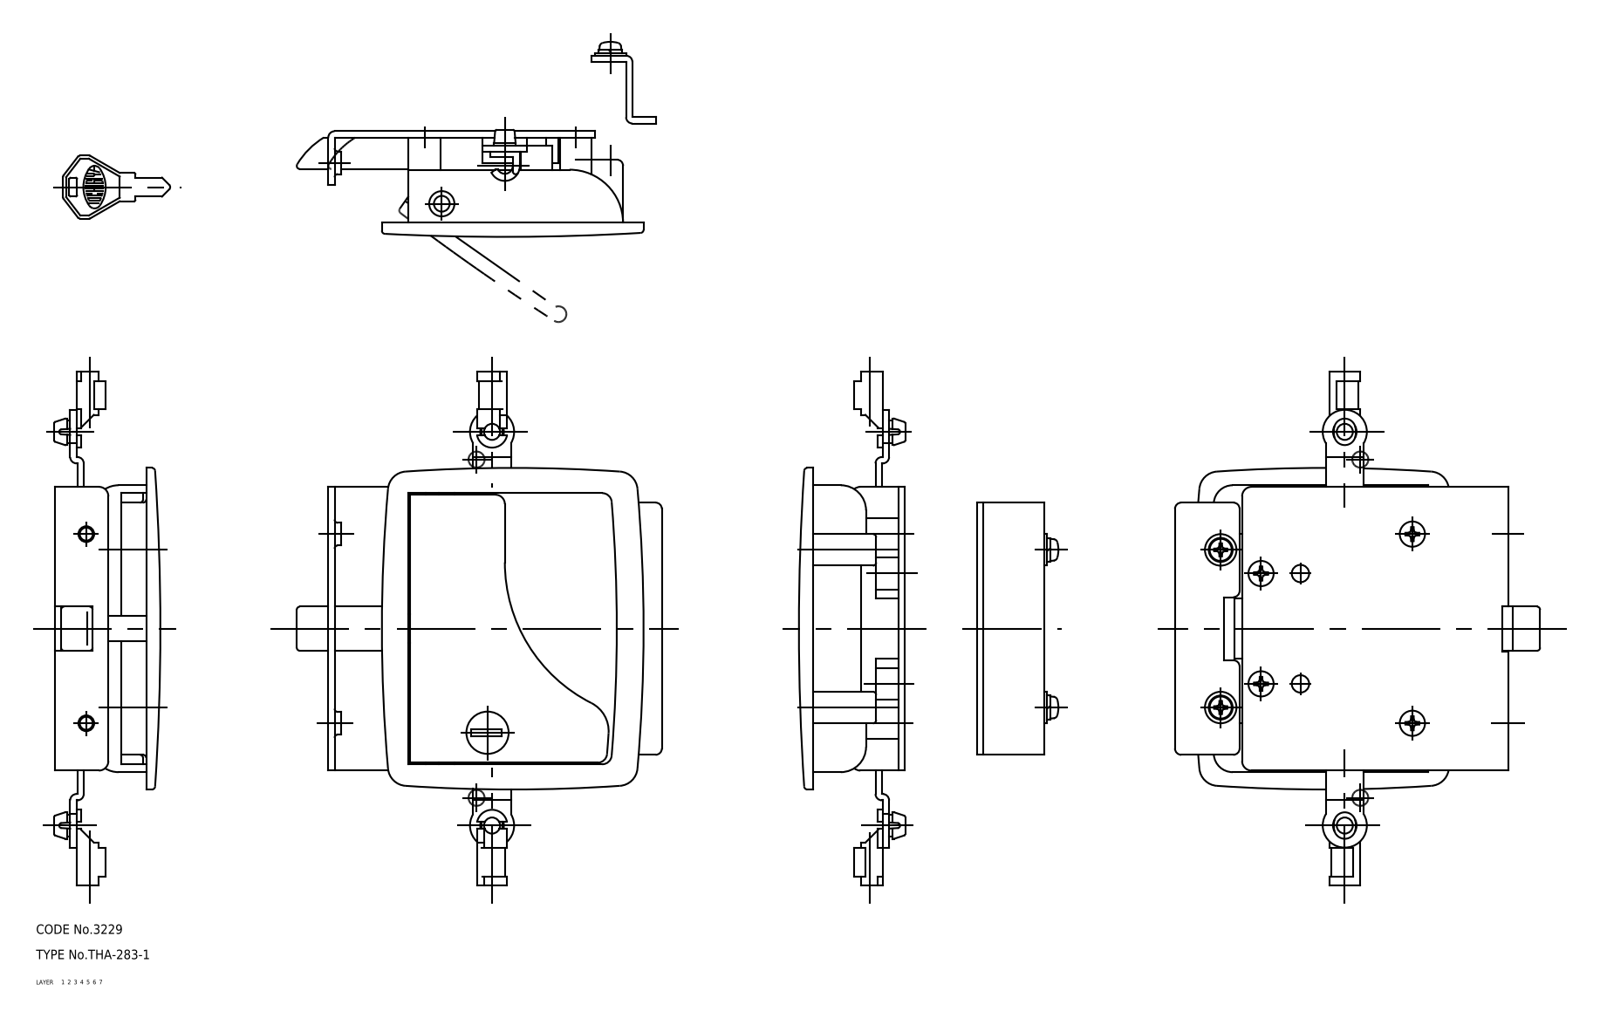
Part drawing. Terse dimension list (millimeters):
name: screw; bracket_B; holder_mr; holder (+8 more)
written by: CADfix (AUTOMOTIVE_DESIGN)
unit: mm
bodies: 15 solids, 807 faces (0 planar, 0 cylindrical, 807 other)
size: 163 × 114.5 × 95.99
volume: 99 624 mm³; area: 81 088 mm²
